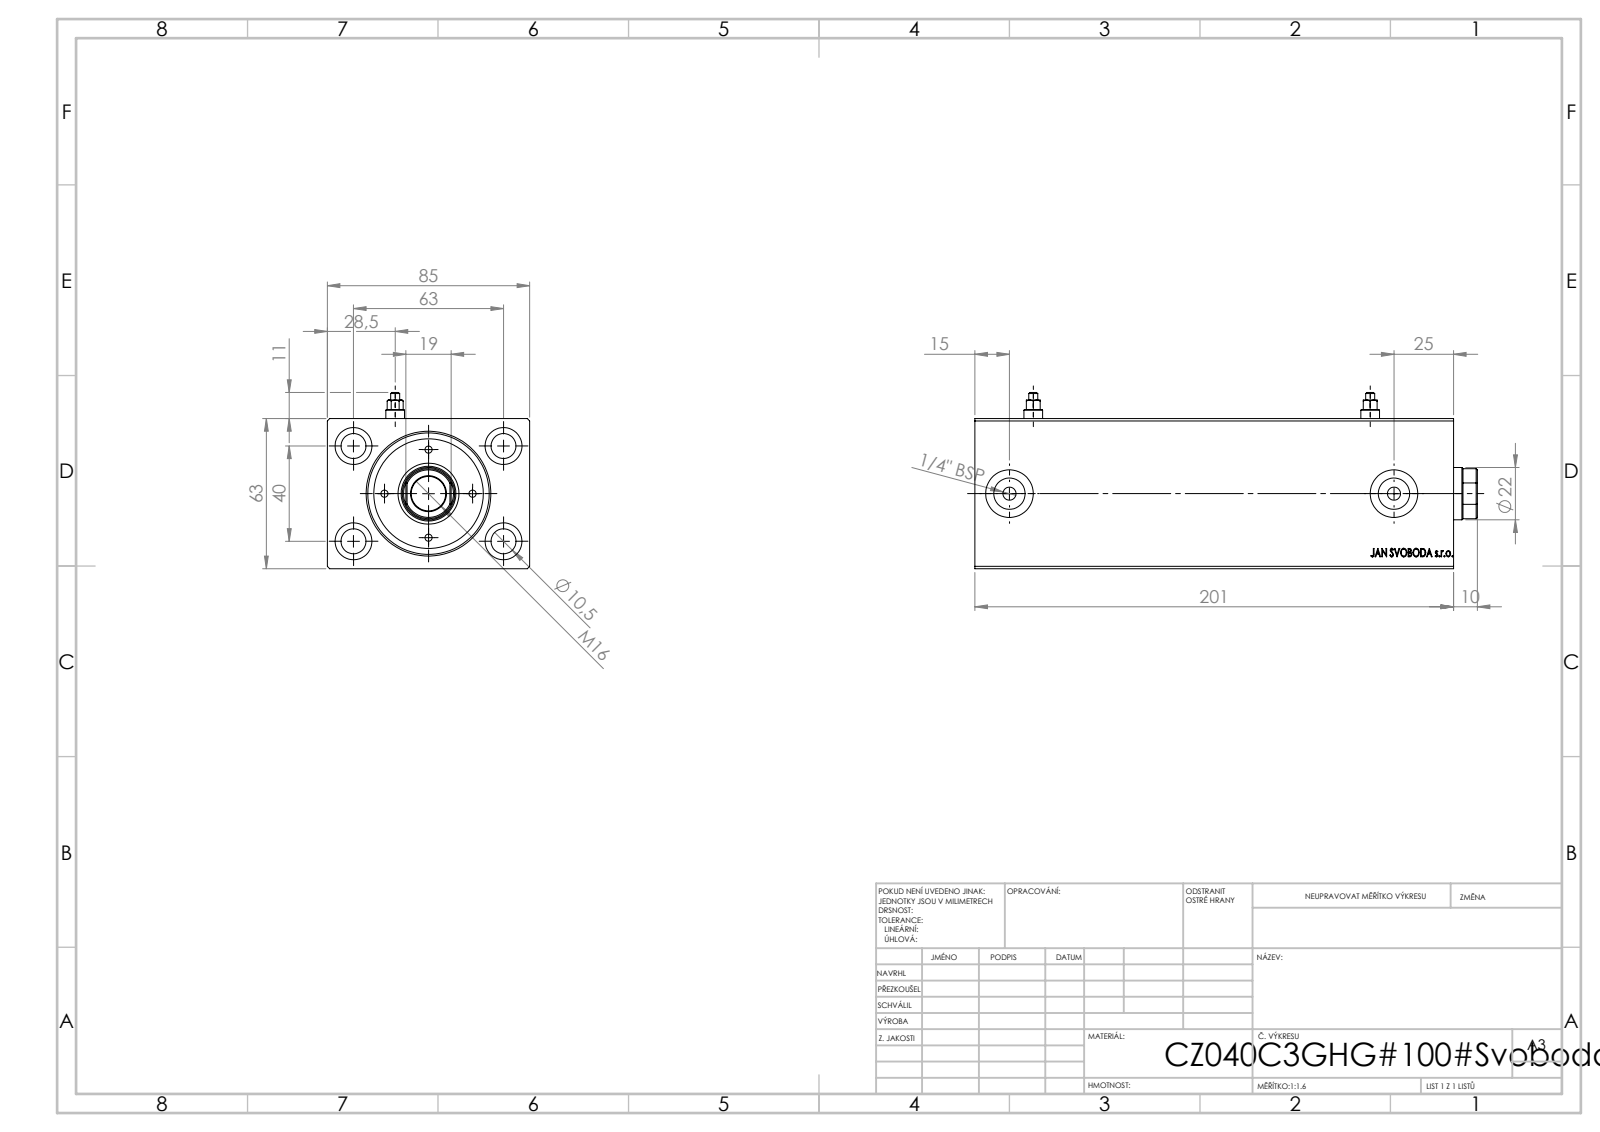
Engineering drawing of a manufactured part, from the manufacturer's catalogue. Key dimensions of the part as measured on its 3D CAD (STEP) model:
STEP written by: SolidWorks 2019 (CONFIG_CONTROL_DESIGN)
Units: millimetres
Bodies: 1 solid, 825 faces (397 planar, 46 cylindrical, 382 other)
Overall size (bounding box): 201 × 85 × 63
Volume: 752 254 mm³ · Surface area: 122 068 mm²
Round holes (diameter × count): ⌀10.5 ×4, ⌀15.5 ×4, ⌀5.5 ×2, ⌀8 ×2, ⌀13.16 ×2, ⌀20 ×2, ⌀36 ×1, ⌀40 ×1, ⌀51 ×1
Main face-to-face distances: 63, 85, 201, 185.7, 15.3, 200.8, 15.1, 10.33, 190.67, 10
Hole centre spacings: 37.31, 40, 63, 74.63, 141.5, 161.5
